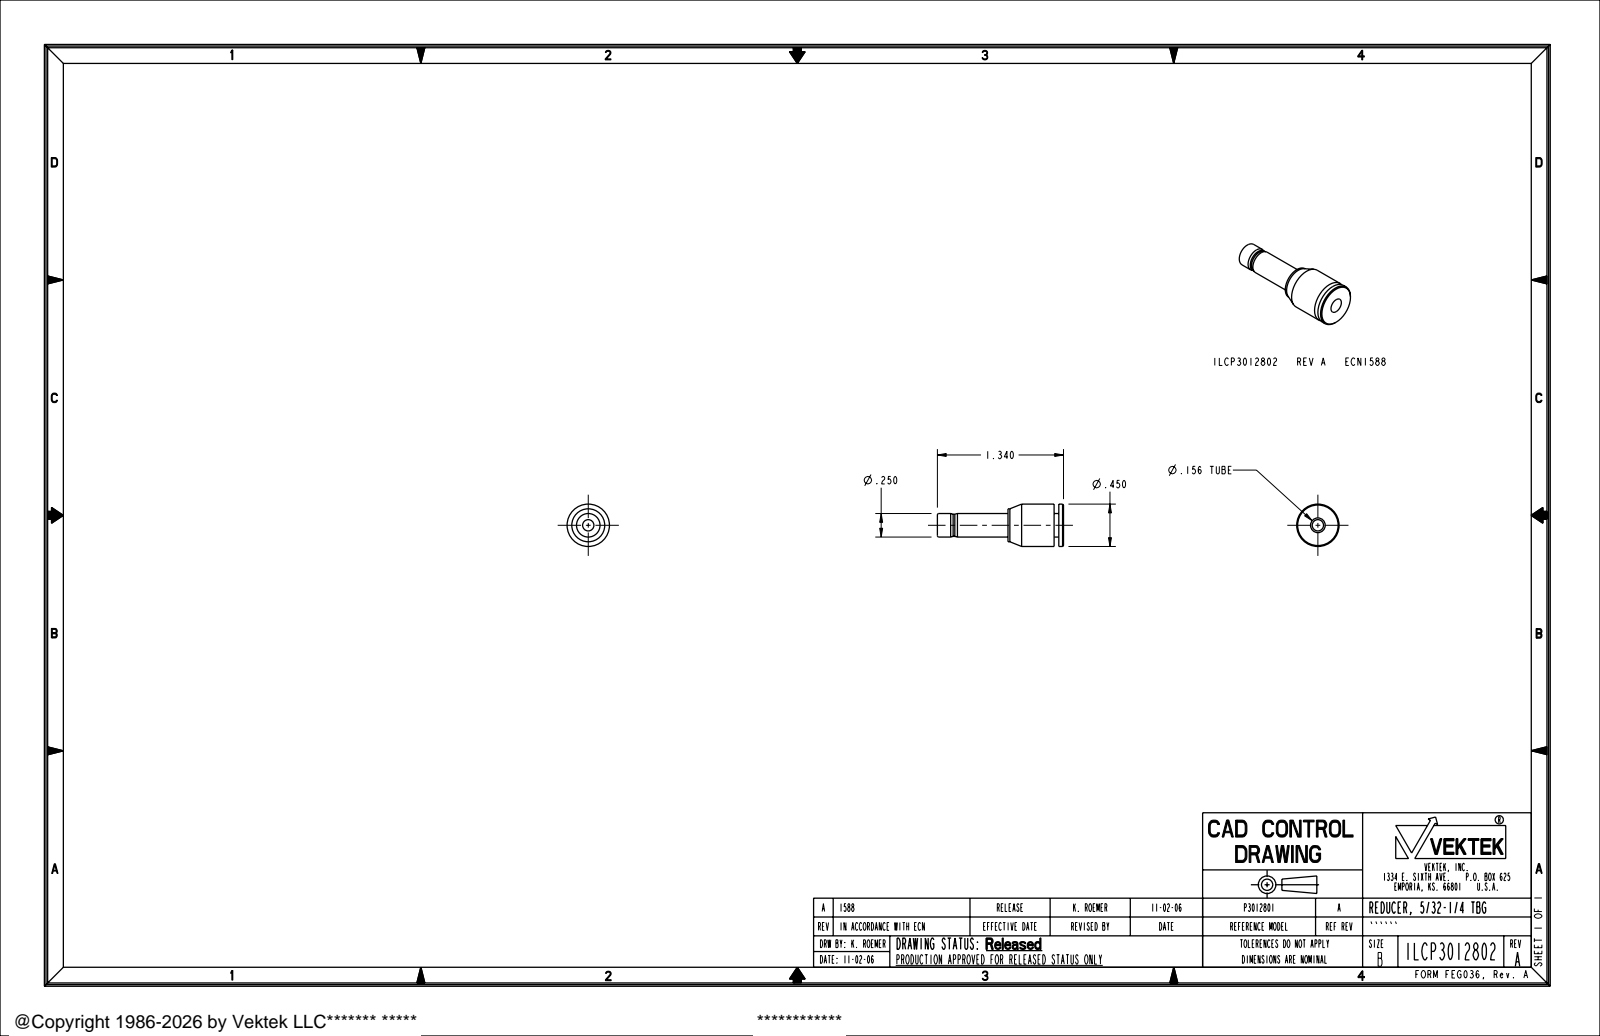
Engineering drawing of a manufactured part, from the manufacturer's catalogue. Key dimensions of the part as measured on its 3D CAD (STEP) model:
Part name (STEP PRODUCT): ILCP3012802
STEP written by: PRO/ENGINEER BY PARAMETRIC TECHNOLOGY CORPORATION, 2005180 (AUTOMOTIVE_DESIGN_CC2)
Units: inches
Bodies: 1 solid, 34 faces (6 planar, 18 cylindrical, 10 other)
Overall size (bounding box): 1.34 × 0.45 × 0.45
Volume: 0.1 in³ · Surface area: 2.378 in²
Round holes (diameter × count): ⌀0.12 ×1, ⌀0.156 ×1
Round bosses / shafts (diameter × count): ⌀0.45 ×1, ⌀0.35 ×1, ⌀0.25 ×1, ⌀0.236 ×1
Main face-to-face distances: 0.05, 0.1, 0.49, 0.54, 0.59, 0.75, 1.24, 1.29, 1.34, 0.84
